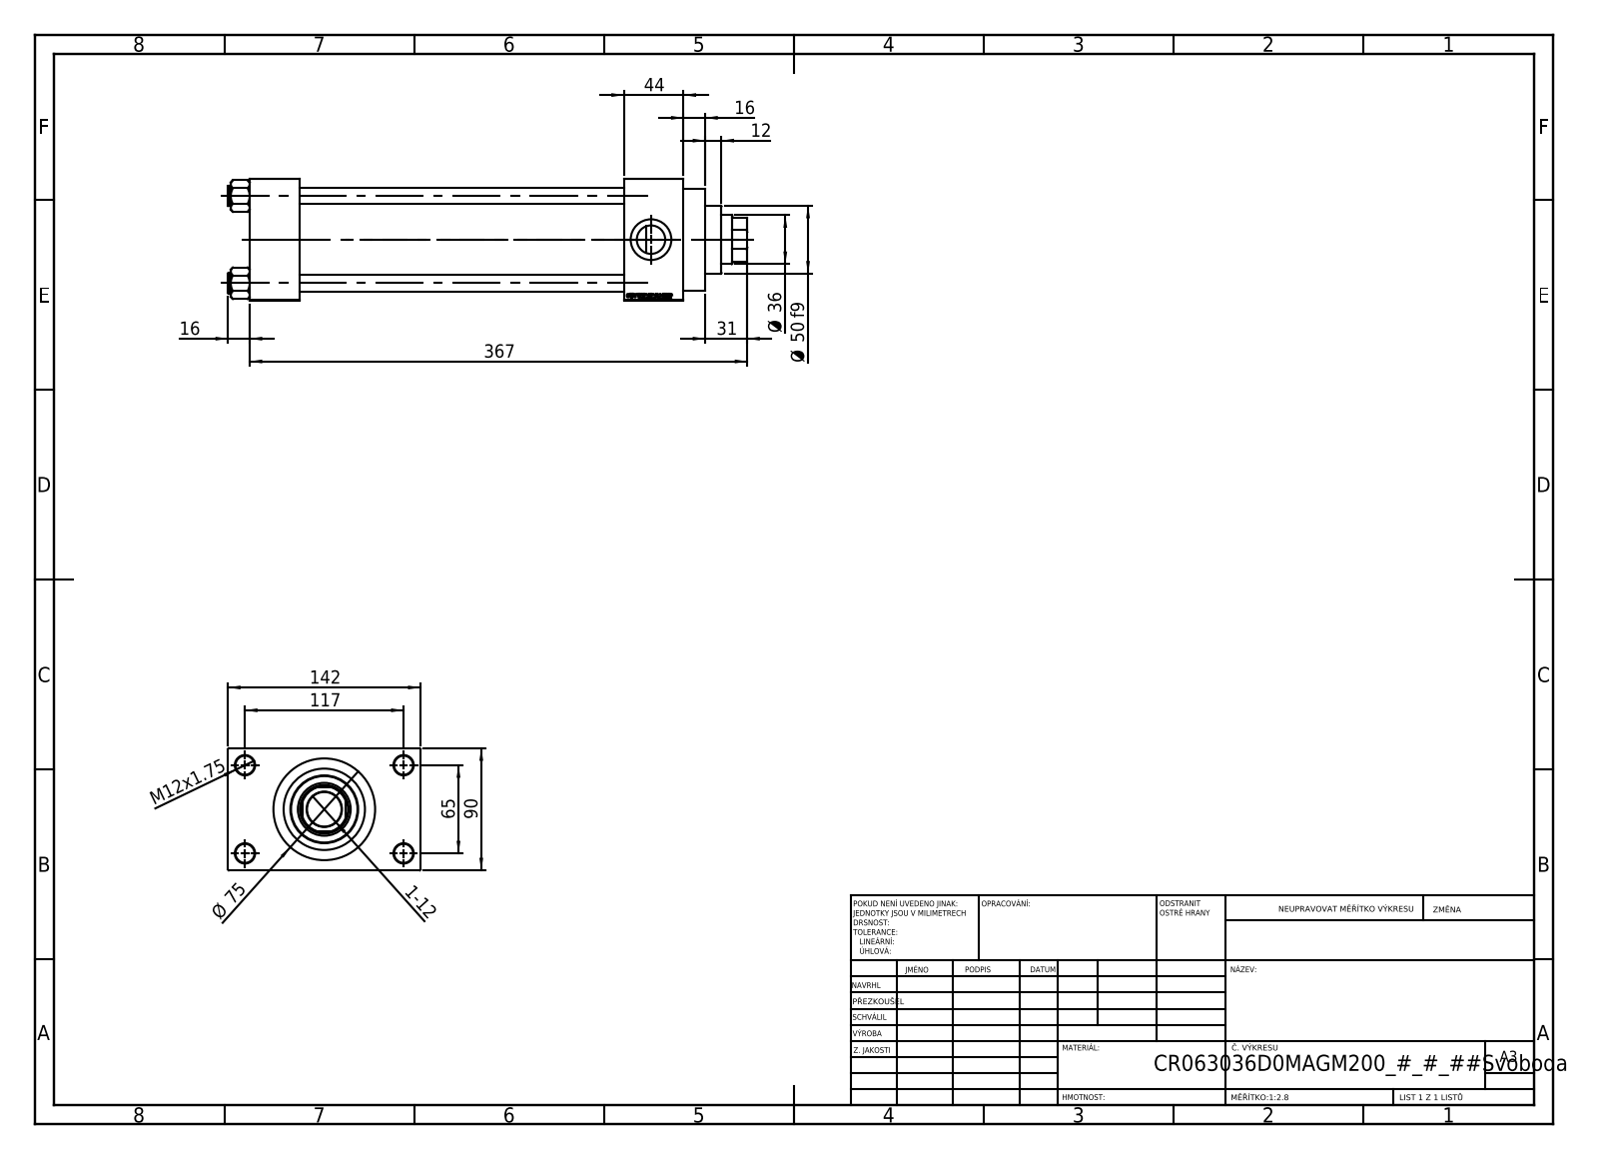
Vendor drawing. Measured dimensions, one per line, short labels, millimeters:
name: V215CR_D_Body; NUT_M5_D; V215_VC_A; V215CR_VCP_D (+1 more)
written by: SolidWorks 2019 (CONFIG_CONTROL_DESIGN)
unit: mm
bodies: 11 solids, 1104 faces (497 planar, 89 cylindrical, 518 other)
size: 383 × 142 × 90
volume: 1 488 000 mm³; area: 327 934 mm²
holes: 4× ⌀12, 4× ⌀14, 2× ⌀7, 2× ⌀20.96, 2× ⌀30, 1× ⌀25.5, 1× ⌀36, 1× ⌀39, 1× ⌀50, 1× ⌀60, 1× ⌀63
bosses: 4× ⌀15, 1× ⌀75, 1× ⌀69
rounds: 1× R17.5
face distances: 90, 239, 37, 276, 320, 283, 44, 26, 116, 142
hole spacings: 26.35, 45.47, 64.3, 66.92, 69.81, 90.65, 111.34, 65
